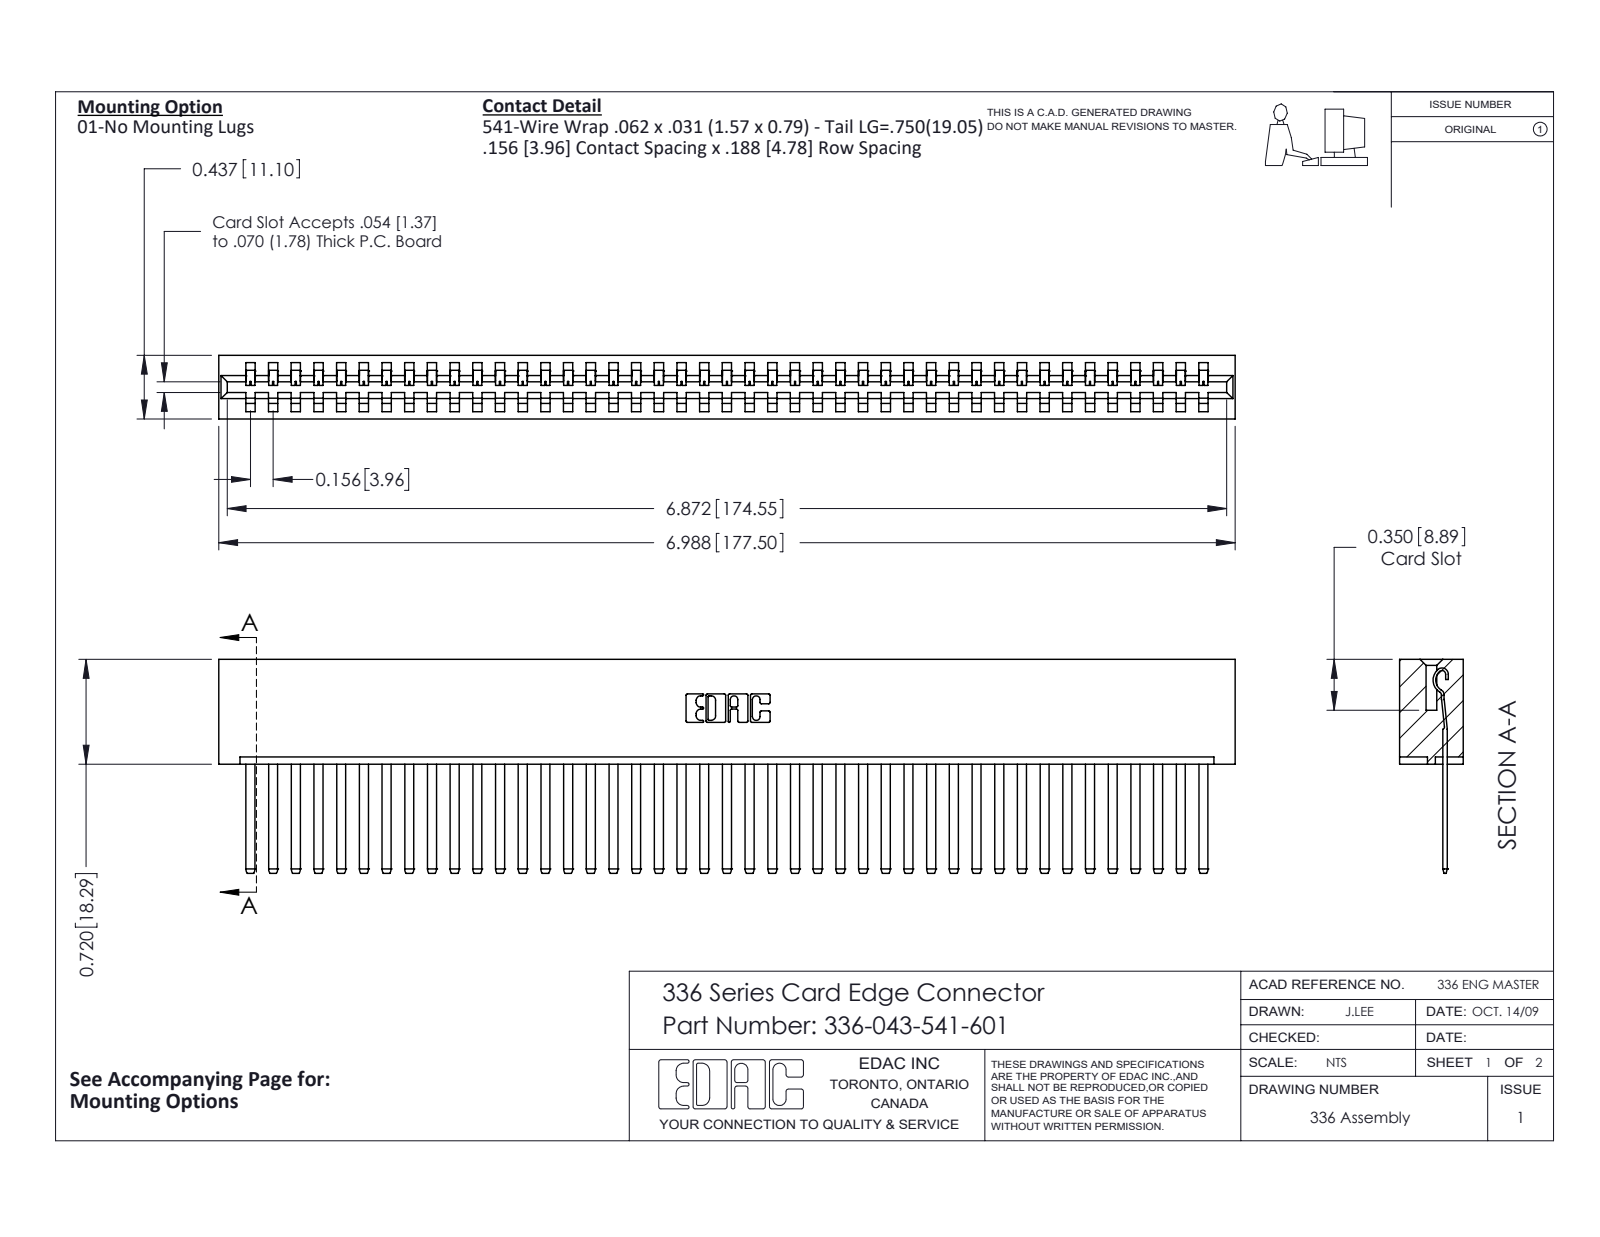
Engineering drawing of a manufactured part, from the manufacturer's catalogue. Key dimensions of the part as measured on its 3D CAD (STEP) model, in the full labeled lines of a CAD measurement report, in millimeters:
Part name (STEP PRODUCT): 336-043-541-601; 336-290-001_336-290-541; 336 Part_Lugless
STEP written by: SolidWorks 2020 (CONFIG_CONTROL_DESIGN)
Units: millimetres
Bodies: 44 solids, 2256 faces (1528 planar, 728 cylindrical, 0 other)
Overall size (bounding box): 177.5 × 37.3 × 11.1
Volume: 27 430 mm³ · Surface area: 29 900 mm²
Partial cylindrical surfaces — rounded edges, fillets, slot ends (radius × count): R0.1 ×86, R1.4 ×86, R0.3 ×22, R0.2 ×6, R0.8 ×6, R0.7 ×3, R0.6 ×2, R1 ×2
Main face-to-face distances: 11.1, 4.6, 8.3, 3.6, 7.5, 2.8, 0.8, 6.5, 1.3, 9.8
